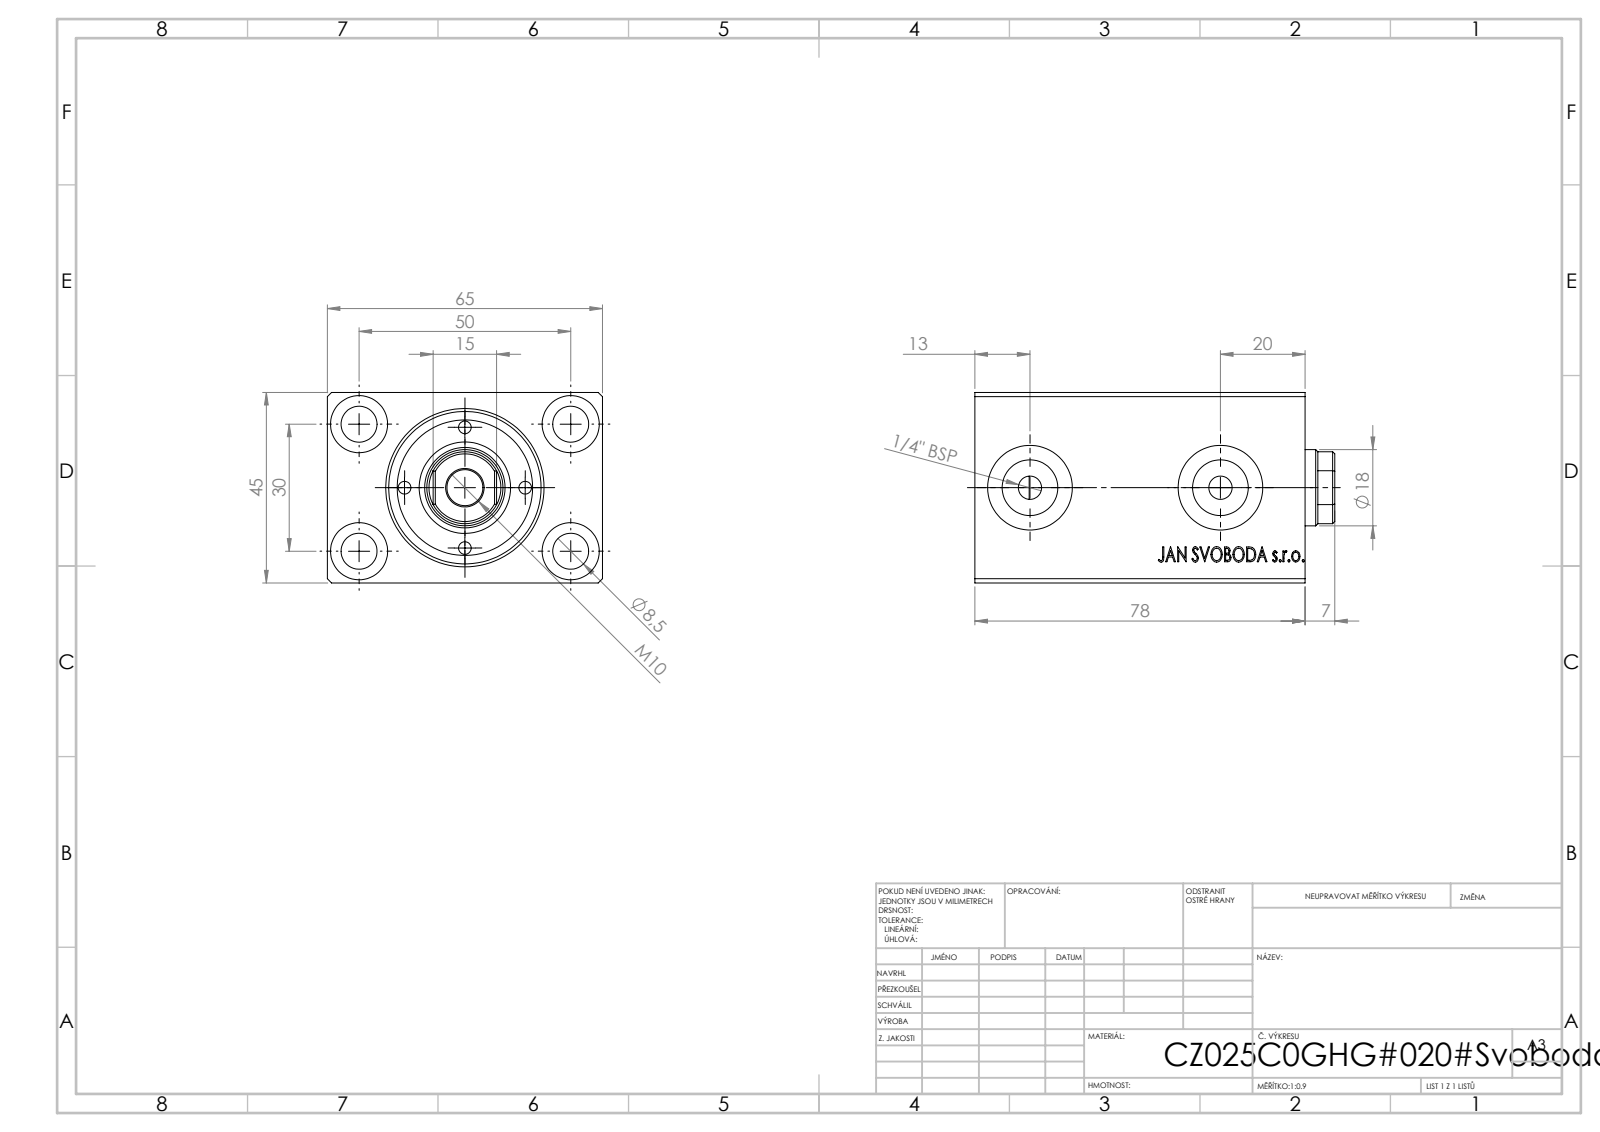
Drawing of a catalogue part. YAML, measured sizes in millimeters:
step_written_by: "SolidWorks 2019 (CONFIG_CONTROL_DESIGN)"
units: millimeters
bodies: {solids: 1, faces: 824, planar: 396, cylindrical: 46, other: 382}
overall_size: [78, 65, 45]
volume: 163100
surface_area: 38790
round_holes:
  - {diameter: 8.5, count: 4}
  - {diameter: 13.5, count: 4}
  - {diameter: 5.5, count: 2}
  - {diameter: 8, count: 2}
  - {diameter: 13.16, count: 2}
  - {diameter: 20, count: 2}
  - {diameter: 25, count: 1}
  - {diameter: 36, count: 1}
face_to_face_distances: [45, 65, 78, 77.8, 10.33, 67.67, 7, 70.8, 71, 65.2]
hole_center_spacings: [29.15, 30, 50, 58.31, 25, 45]
